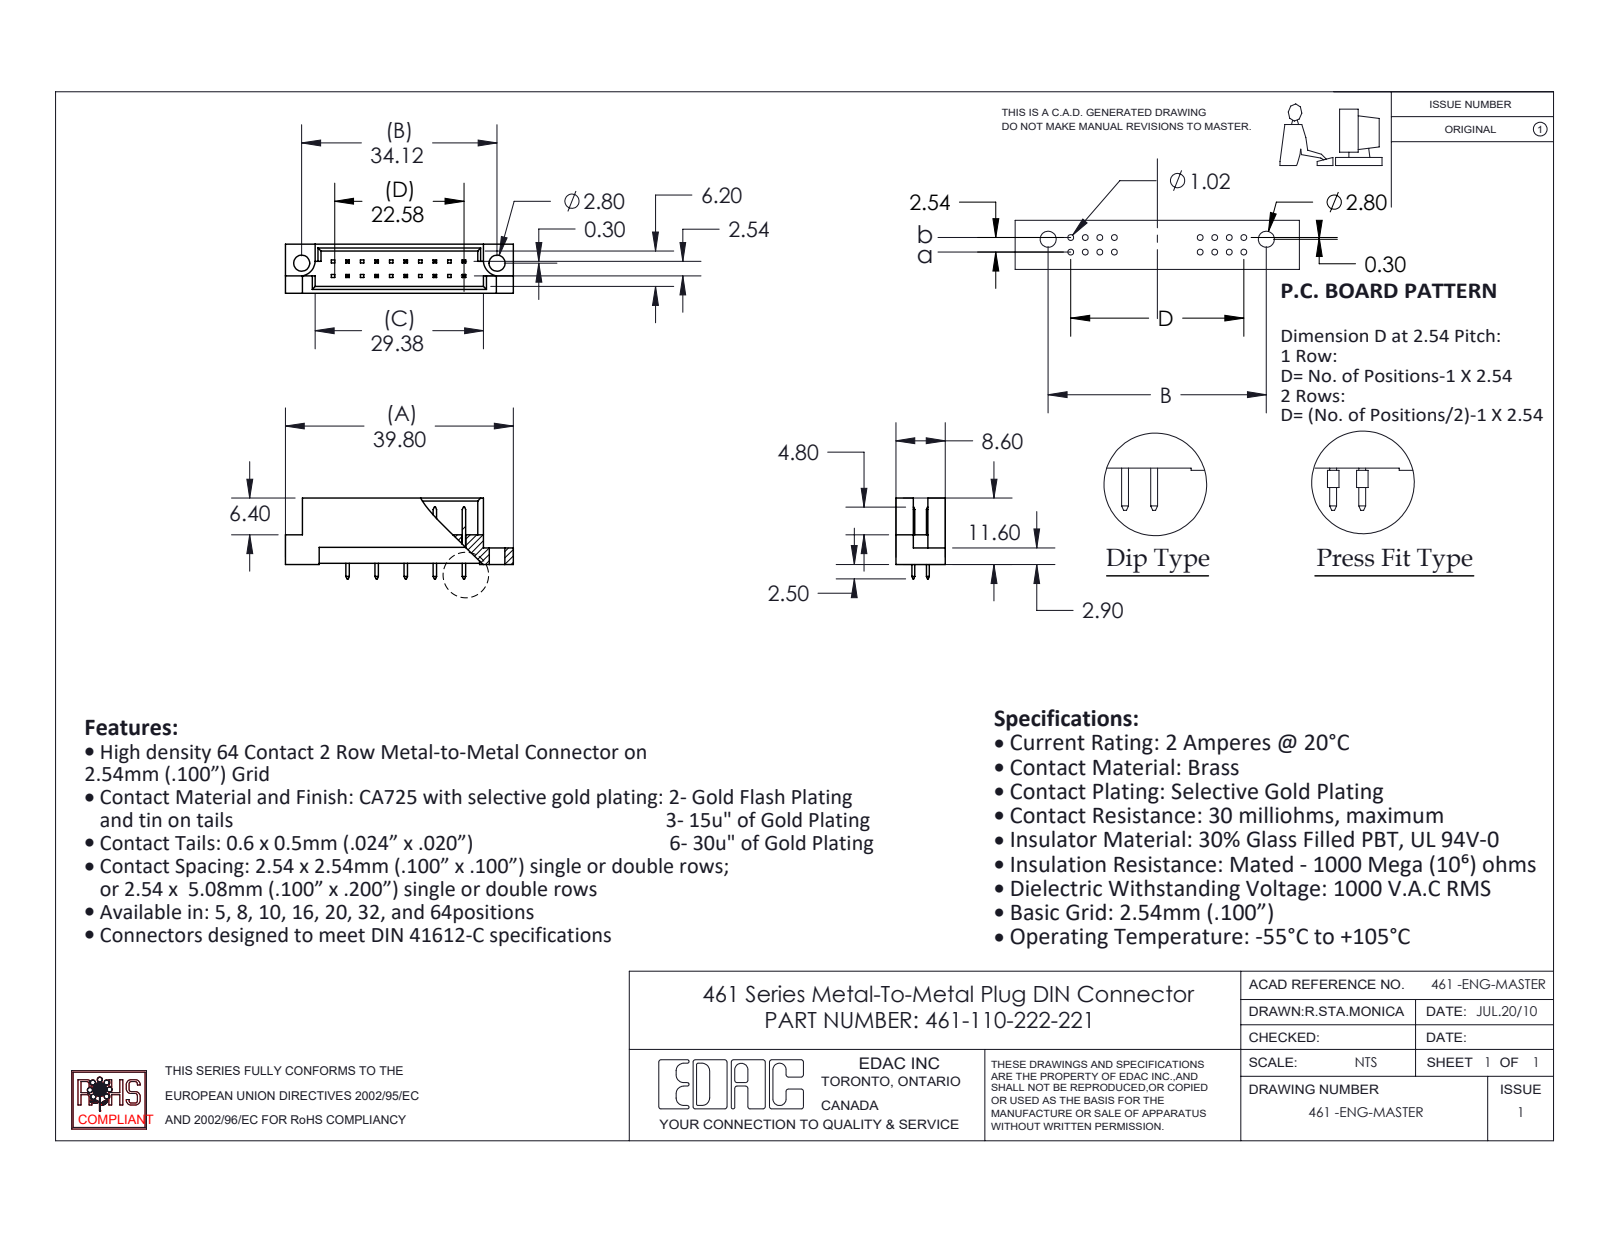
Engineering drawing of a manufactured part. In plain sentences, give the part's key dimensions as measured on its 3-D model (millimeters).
The part is named "461 Part_20; 461-290_22; 461-110-222-221". Its 3-D file was written by "SolidWorks 2020 (CONFIG_CONTROL_DESIGN)". It is 11 solids with 268 faces: 262 planar, 6 cylindrical and 0 other. Overall it measures 39.8 by 14.1 by 8.6 millimeters. Its volume is 1 941 cubic millimeters and its surface area 2 609 square millimeters. Round holes: 2 of diameter 2.8. Partial cylindrical surfaces (rounded edges, fillets, slot ends): 2 of radius 2.8. The main face-to-face distances are 1.2, 7.4, 8.6, 6.2, 5, 2.54, 5.08, 3.28, 5.32, 2.08. The hole center spacings are 34.12.
